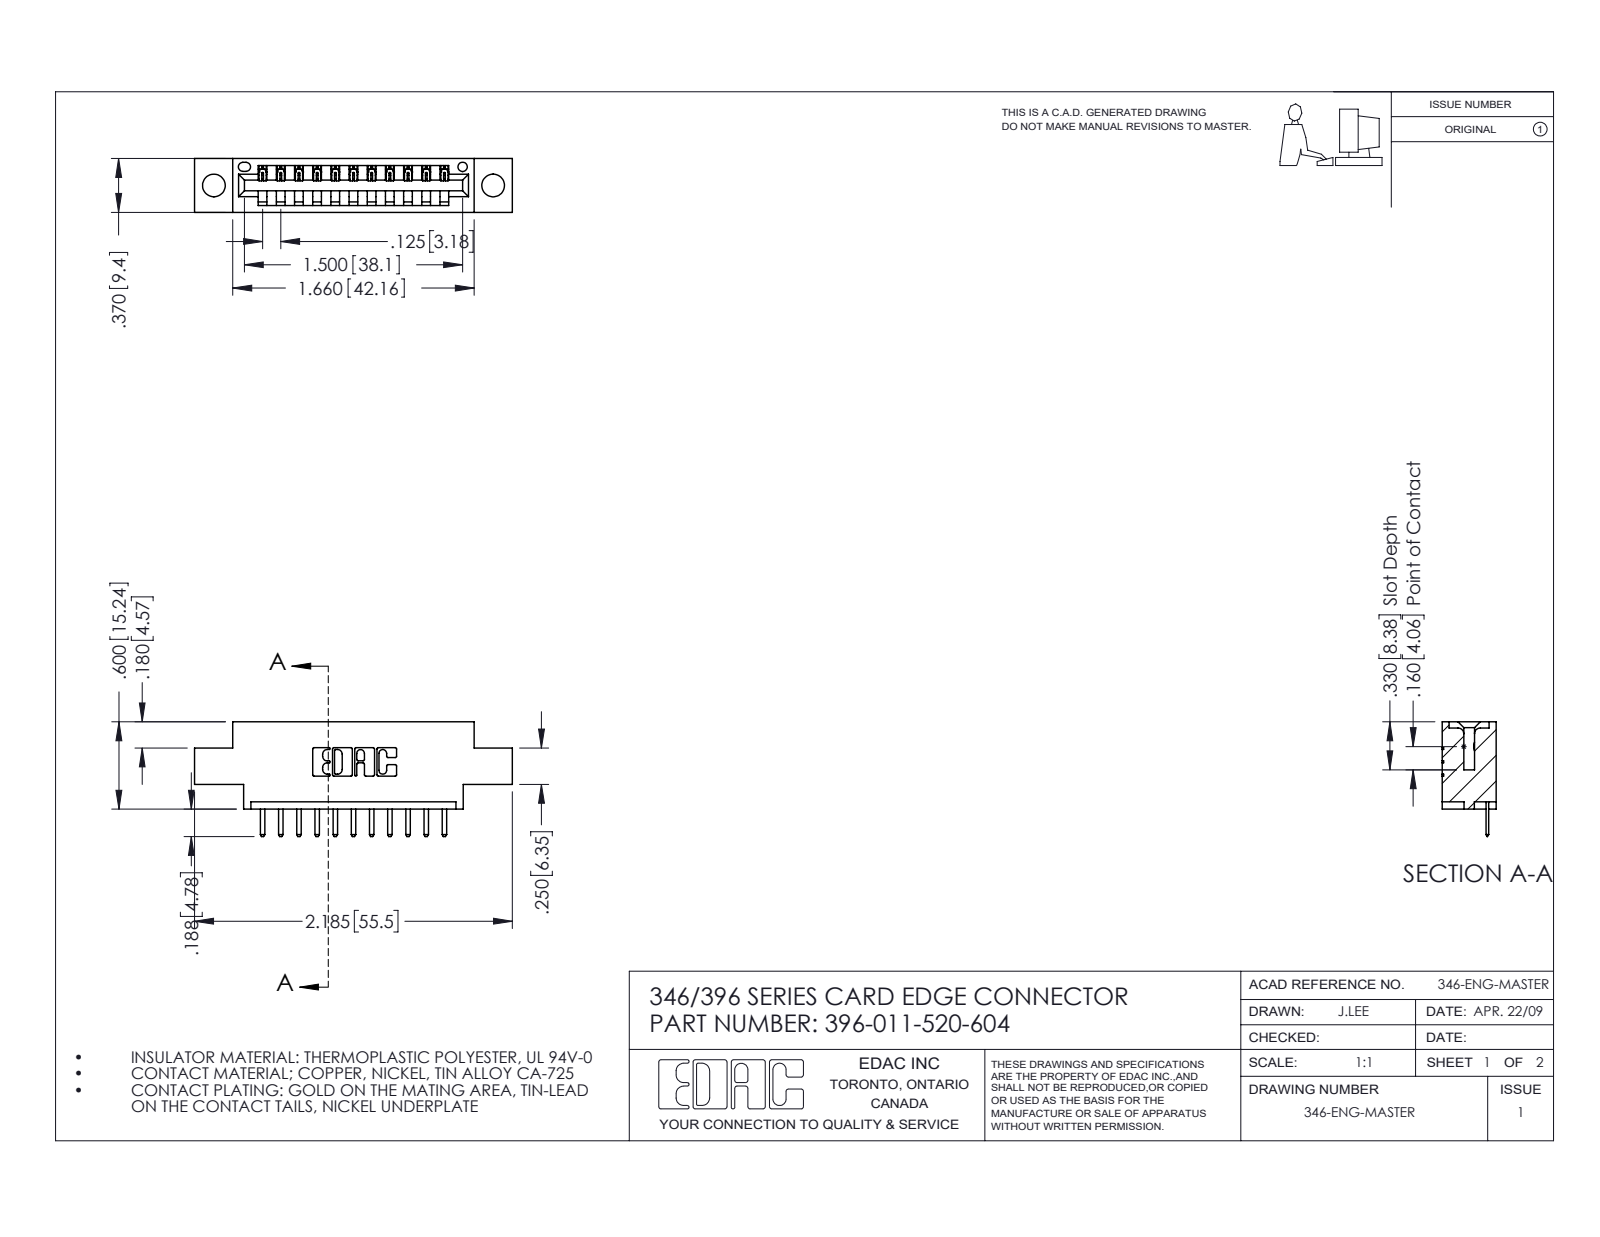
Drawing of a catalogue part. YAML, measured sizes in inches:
part_name: "346 Part_0.170 Offset - 0.156 Dia-TH; 396-011-520-604; 345-292-001_345-293-120"
step_written_by: "SolidWorks 2016 (CONFIG_CONTROL_DESIGN)"
units: inches
bodies: {solids: 12, faces: 808, planar: 542, cylindrical: 266, other: 0}
overall_size: [2.185, 0.788, 0.37]
volume: 0.294
surface_area: 8.611
round_holes:
  - {diameter: 0.156, count: 2}
  - {diameter: 0.064, count: 1}
partial_cylinders:
  - {radius: 0.01, count: 24}
  - {radius: 0.006, count: 22}
  - {radius: 0.01, count: 22}
  - {radius: 0.007, count: 6}
  - {radius: 0.031, count: 6}
  - {radius: 0.026, count: 3}
  - {radius: 0.031, count: 2}
  - {radius: 0.04, count: 2}
face_to_face_distances: [0.25, 0.37, 0.048, 0.322, 0.148, 0.222, 0.1, 0.174, 0.072, 0.298]
hole_center_spacings: [0.246, 1.715, 1.92]
